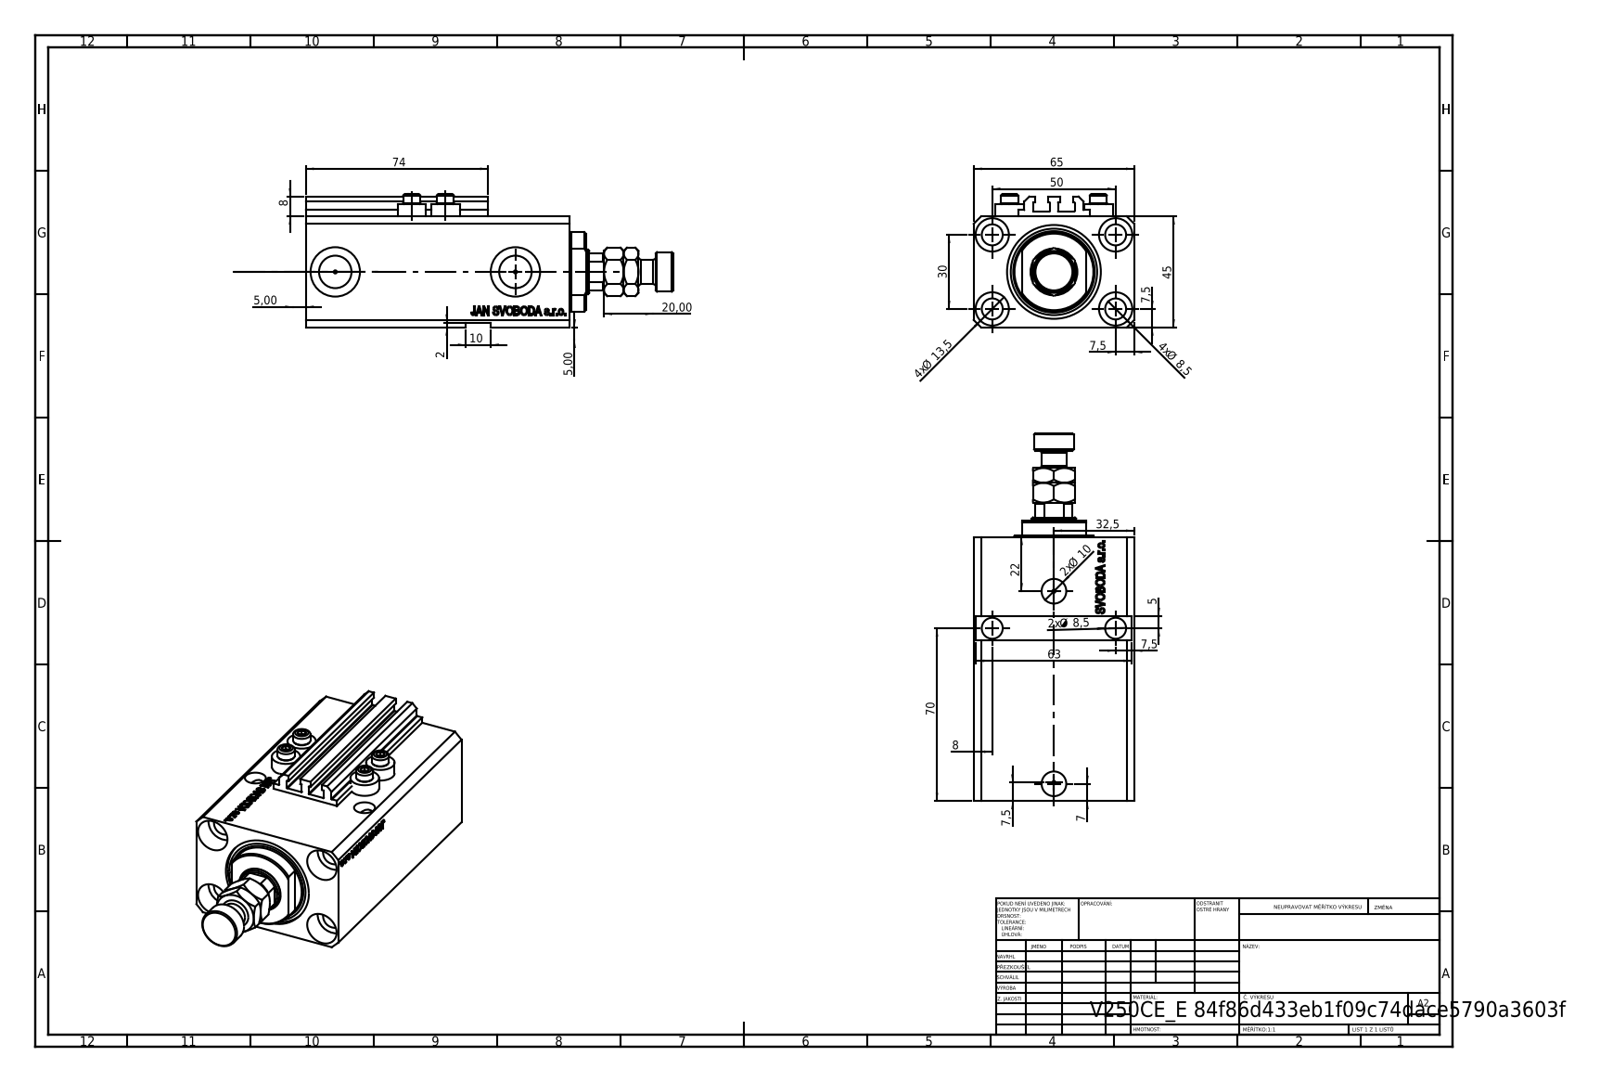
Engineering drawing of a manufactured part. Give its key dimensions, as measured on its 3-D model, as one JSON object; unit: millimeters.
{"part_name": "ALLEN BOLT V250CE; V250CE_E; V250CE_VC_E; V250CE_C_VCP (+1 more)", "step_written_by": "SolidWorks 2019 (CONFIG_CONTROL_DESIGN)", "units": "millimeters", "bodies": {"solids": 9, "faces": 1119, "planar": 527, "cylindrical": 130, "other": 462}, "overall_size": [148.9, 65, 54], "volume_mm3": 282285, "surface_area_mm2": 80025, "round_holes": [[8.5, 7], [1.25, 4], [4, 4], [13.5, 4], [10, 2], [13.16, 2], [20, 2], [18, 1], [25, 1], [38, 1]], "round_bosses_or_shafts": [[11.6, 4], [7, 4], [16, 1], [10, 1]], "partial_cylinders_radius": [[0.2, 10], [8.5, 1], [16, 1]], "face_to_face_distances": [45, 65, 81.9, 2, 47, 6.9, 107, 25.1, 2.5, 75], "hole_center_spacings": [29.15, 50, 13.6, 15.12, 27.89, 30, 33.62, 36]}
